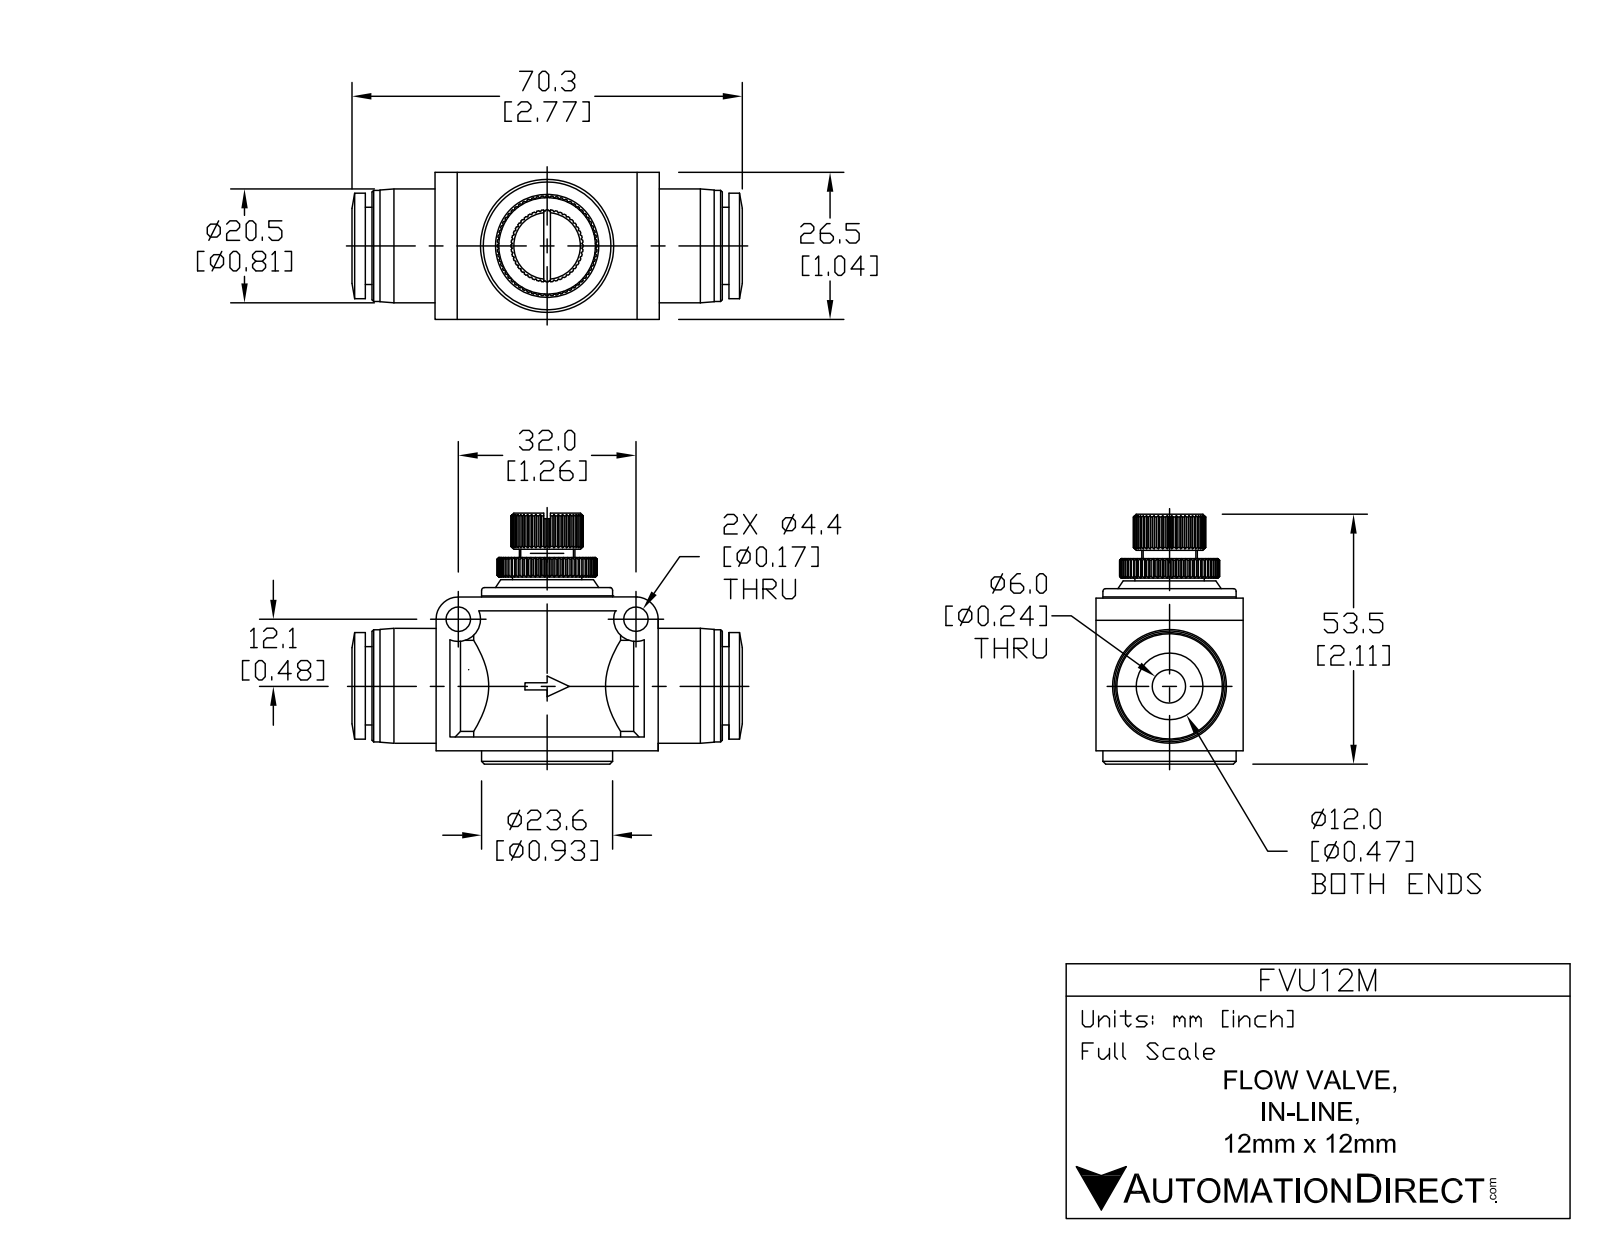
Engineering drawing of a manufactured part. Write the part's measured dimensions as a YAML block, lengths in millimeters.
part_name: "FVU12M"
step_written_by: "SolidWorks 2015 (AUTOMOTIVE_DESIGN)"
units: millimeters
bodies: {solids: 1, faces: 615, planar: 287, cylindrical: 166, other: 162}
overall_size: [73.5, 53.5, 26.5]
volume: 31220
surface_area: 14430
round_holes:
  - {diameter: 4.4, count: 2}
  - {diameter: 10, count: 1}
  - {diameter: 12.3, count: 1}
round_bosses_or_shafts:
  - {diameter: 24, count: 1}
  - {diameter: 20.5, count: 1}
  - {diameter: 20, count: 1}
  - {diameter: 19, count: 1}
  - {diameter: 16.7, count: 1}
  - {diameter: 13.9, count: 1}
  - {diameter: 12.5, count: 1}
  - {diameter: 10, count: 1}
partial_cylinders:
  - {radius: 4, count: 2}
  - {radius: 6.5, count: 1}
  - {radius: 9, count: 1}
  - {radius: 13.6, count: 1}
face_to_face_distances: [2.5, 2.4, 25, 29.9, 27.5, 26.5, 4.9, 26.3, 37.9, 40.4]
hole_center_spacings: [32.4]
